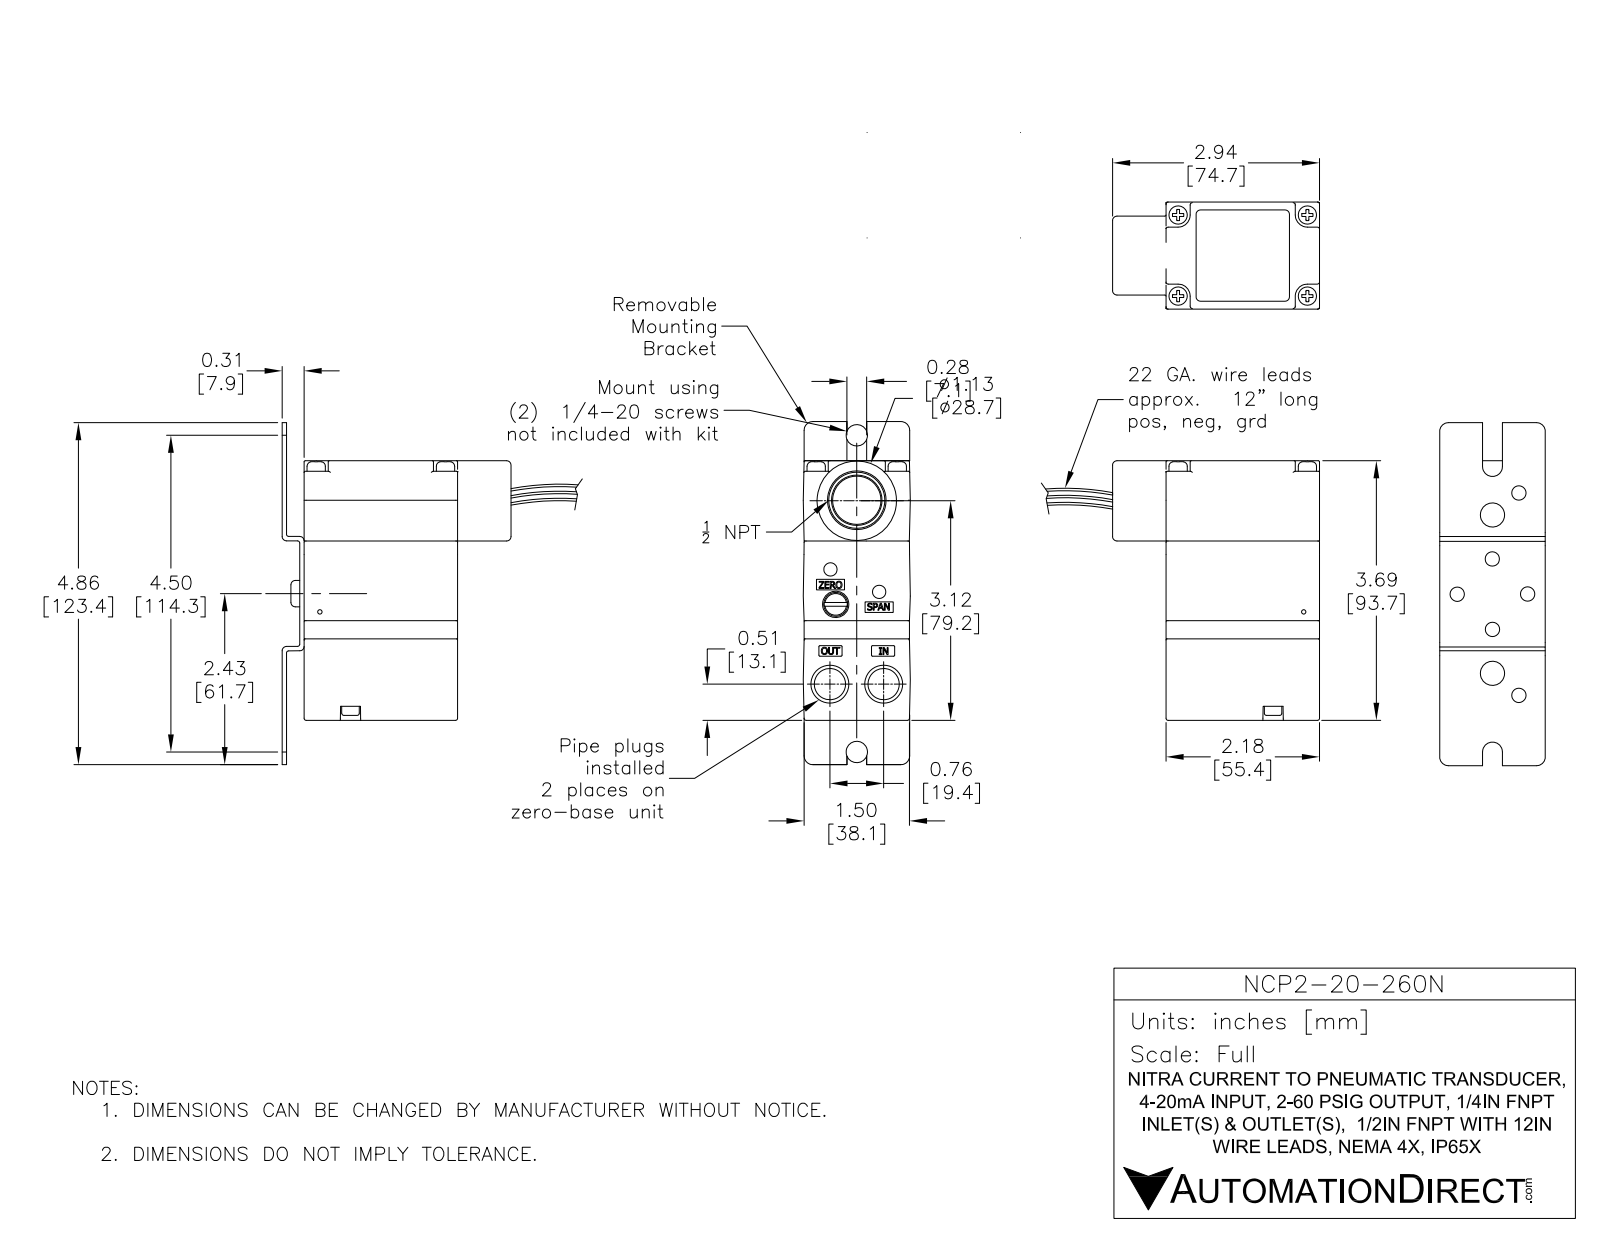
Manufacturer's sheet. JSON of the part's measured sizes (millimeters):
{"part_name": "NCP2-20-260N", "step_written_by": "SolidWorks 2016 (AUTOMOTIVE_DESIGN)", "units": "millimeters", "bodies": {"solids": 4, "faces": 1003, "planar": 537, "cylindrical": 291, "other": 175}, "overall_size": [124.1, 83.35, 39.12], "volume_mm3": 189475, "surface_area_mm2": 49479, "round_holes": [[5.16, 6], [3.37, 3], [3.18, 2], [3.3, 2], [4.8, 2], [8.73, 2], [11.38, 2], [1.59, 1], [3.17, 1], [7.37, 1], [17.48, 1], [20.07, 1]], "round_bosses_or_shafts": [[6.6, 4], [6.35, 3], [7.49, 2], [28.95, 1], [16.18, 1], [11.43, 1], [8.66, 1]], "partial_cylinders_radius": [[0.76, 56], [0.5, 17], [0.4, 8], [1.59, 8], [3.17, 8], [1.47, 6], [1.25, 4], [1.27, 4]], "face_to_face_distances": [1.59, 6.75, 7.03, 8.62, 55.55, 37.35, 38.74, 1.39, 55.54, 62.57], "hole_center_spacings": [25.4, 12.4, 15.87, 17.74, 17.94, 17.96, 18.41, 18.78]}
